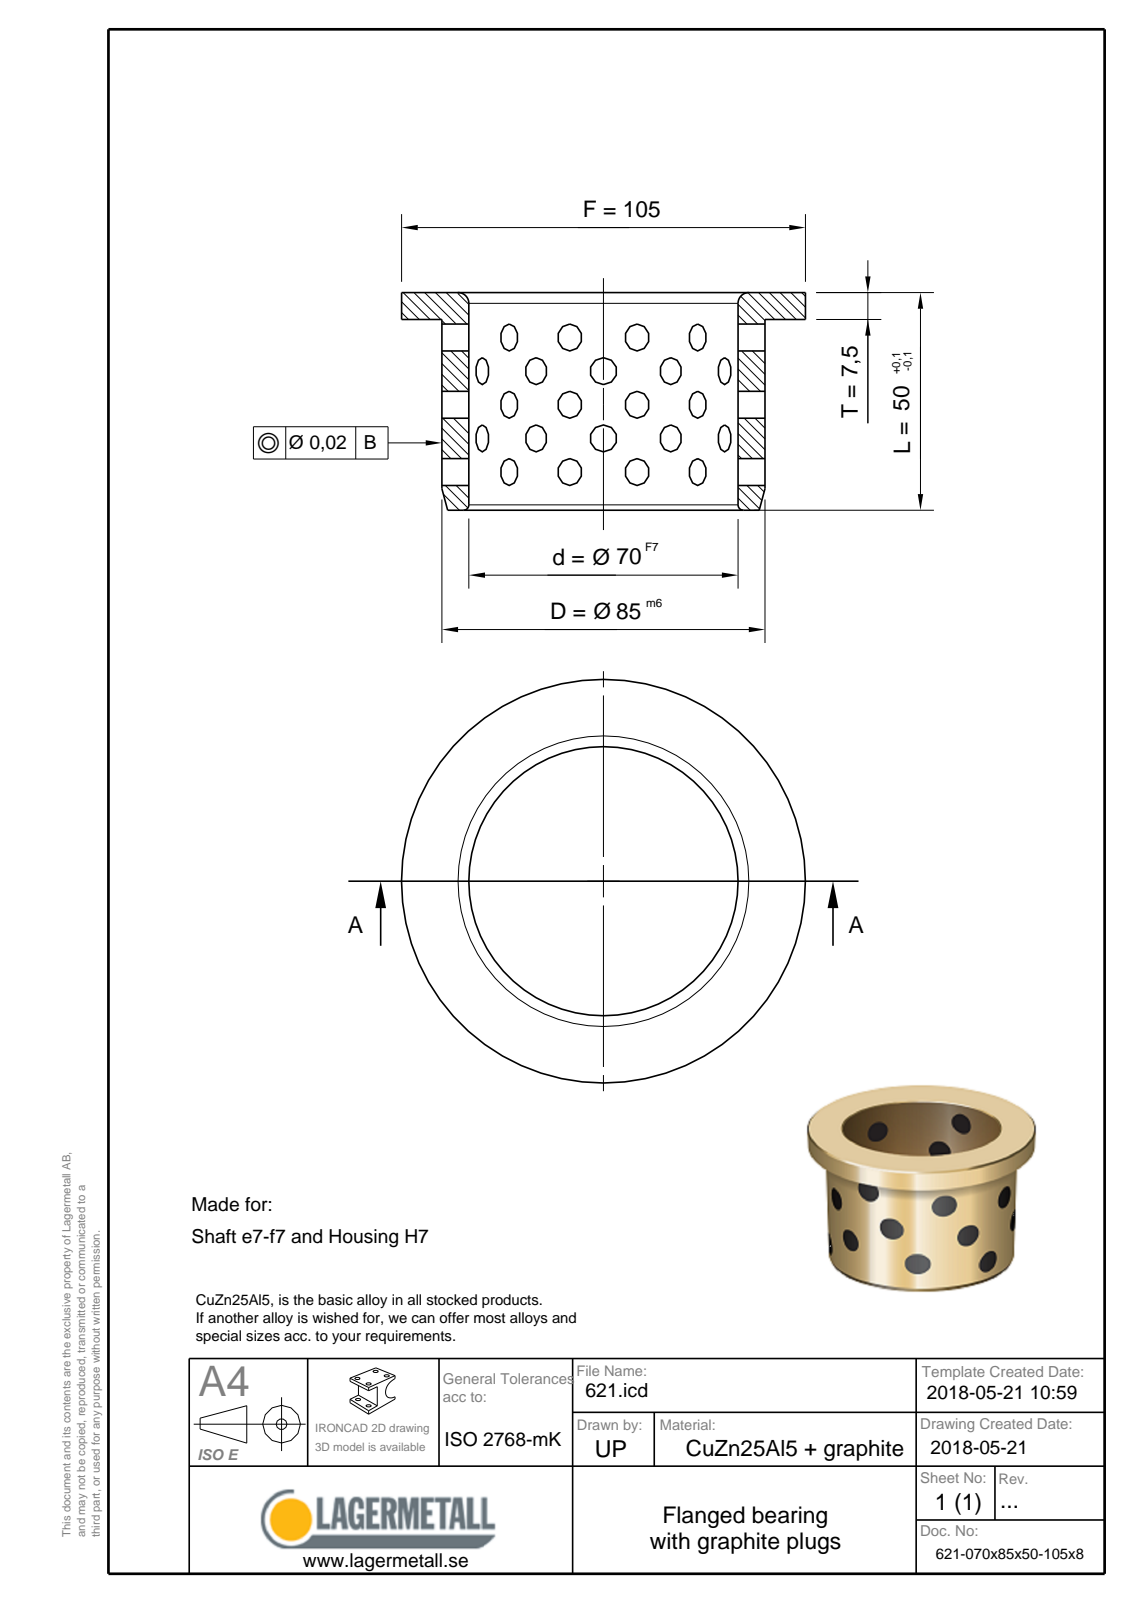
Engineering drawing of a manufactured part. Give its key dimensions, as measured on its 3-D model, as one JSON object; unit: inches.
{"part_name": "621-070x85x50-105x8", "step_written_by": "Spatial InterOp 3D (CONFIG_CONTROL_DESIGN)", "units": "inches", "bodies": {"solids": 1, "faces": 9, "planar": 3, "cylindrical": 3, "other": 3}, "overall_size": [4.134, 4.134, 1.969], "volume_in3": 6.884, "surface_area_in2": 52.28, "round_holes": [[2.756, 1]], "round_bosses_or_shafts": [[4.134, 1], [3.346, 1]], "face_to_face_distances": [0.295, 1.673, 1.969]}
